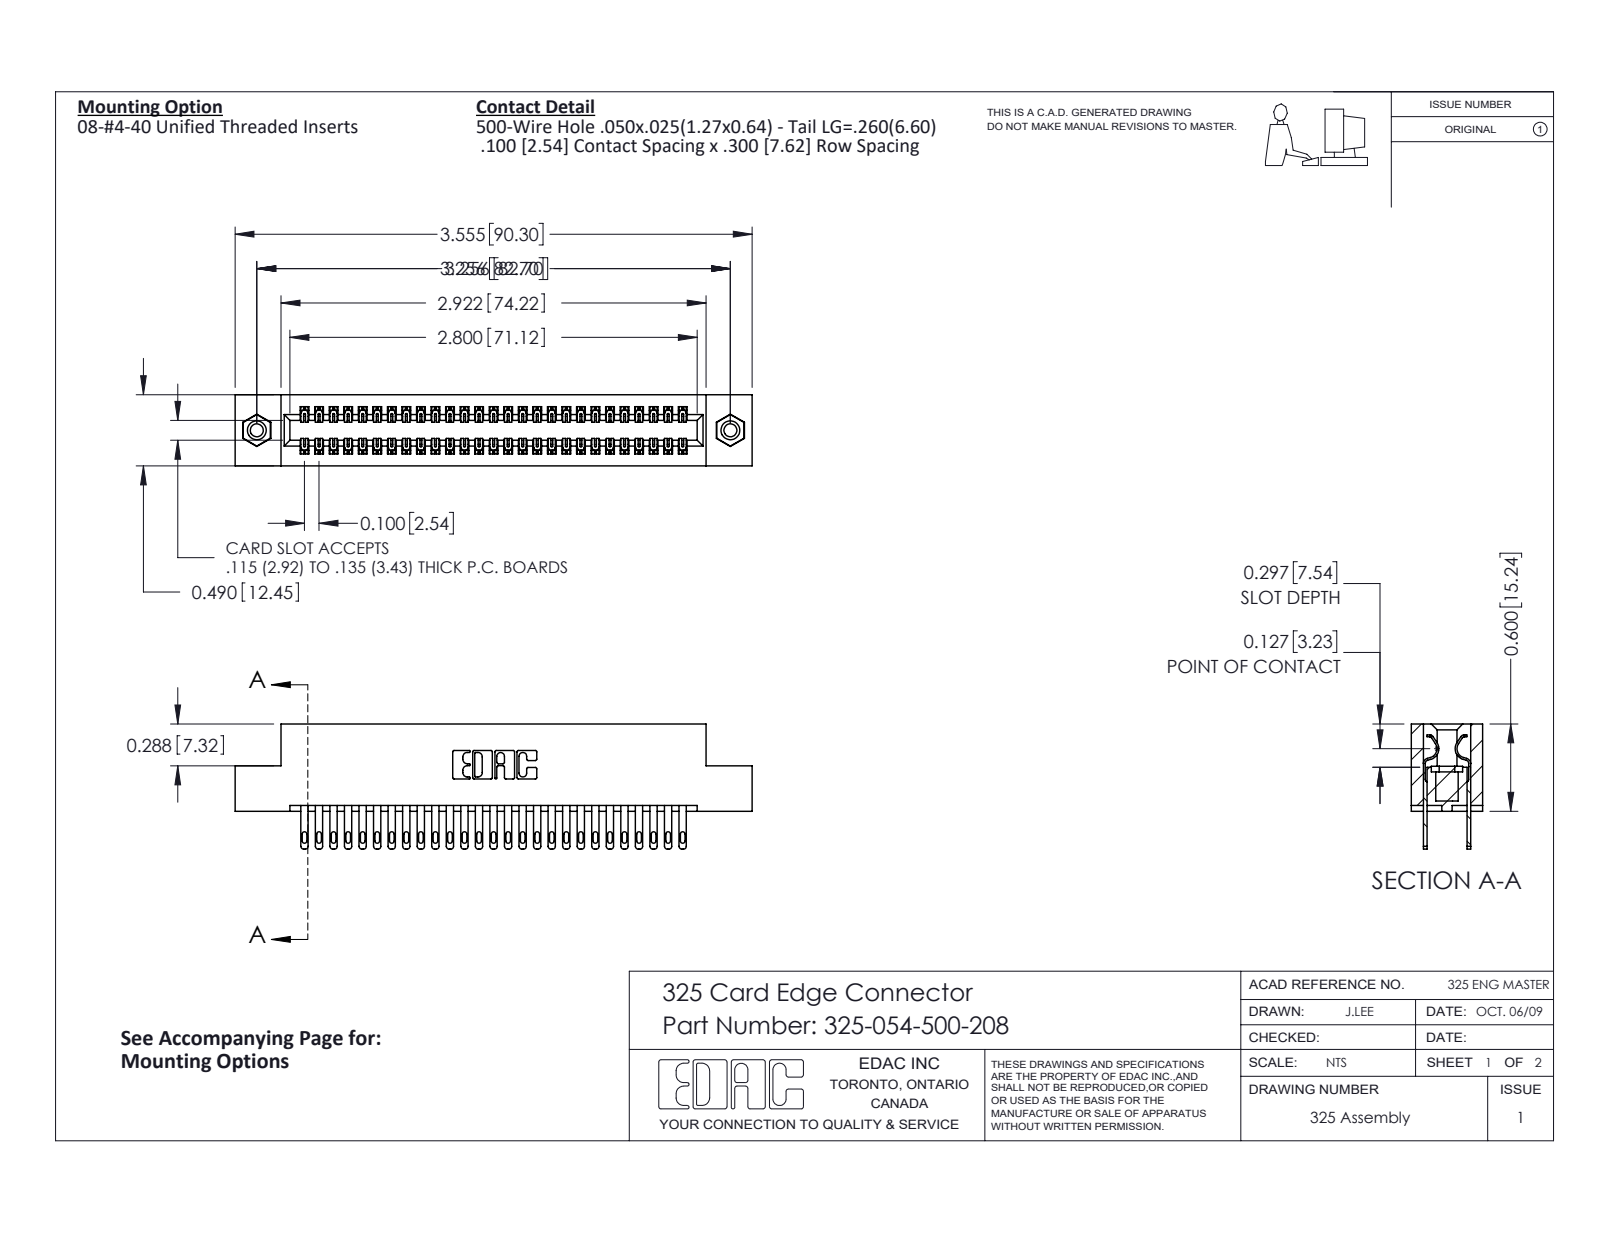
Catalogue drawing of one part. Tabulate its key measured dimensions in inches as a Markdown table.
| quantity | value |
| --- | --- |
| part name | 325-292-001_325-293-100; 325 Part_TI; 325-054-500-208; 345-250-001_345-250-003-102 |
| STEP written by | SolidWorks 2016 (CONFIG_CONTROL_DESIGN) |
| units | inches |
| bodies | 57 solids, 2766 faces (1722 planar, 1028 cylindrical, 16 other) |
| overall size | 3.555 × 0.86 × 0.49 |
| volume | 0.713 in³ |
| surface area | 22.26 in² |
| round holes (diameter × count) | 0.089 × 2, 0.125 × 2, 0.16 × 2 |
| round bosses / shafts (diameter × count) | 0.155 × 2 |
| partial cylindrical surfaces (radius × count) | 0.006 × 81, 0.016 × 54, 0.02 × 54, 0.01 × 22, 0.007 × 6, 0.031 × 6, 0.026 × 3, 0.014 × 2 |
| main face-to-face distances | 0.083, 0.407, 0.3, 0.107, 0.383, 0.025, 0.49, 0.325, 0.275, 0.04 |
| hole center spacings | 3.256 |
